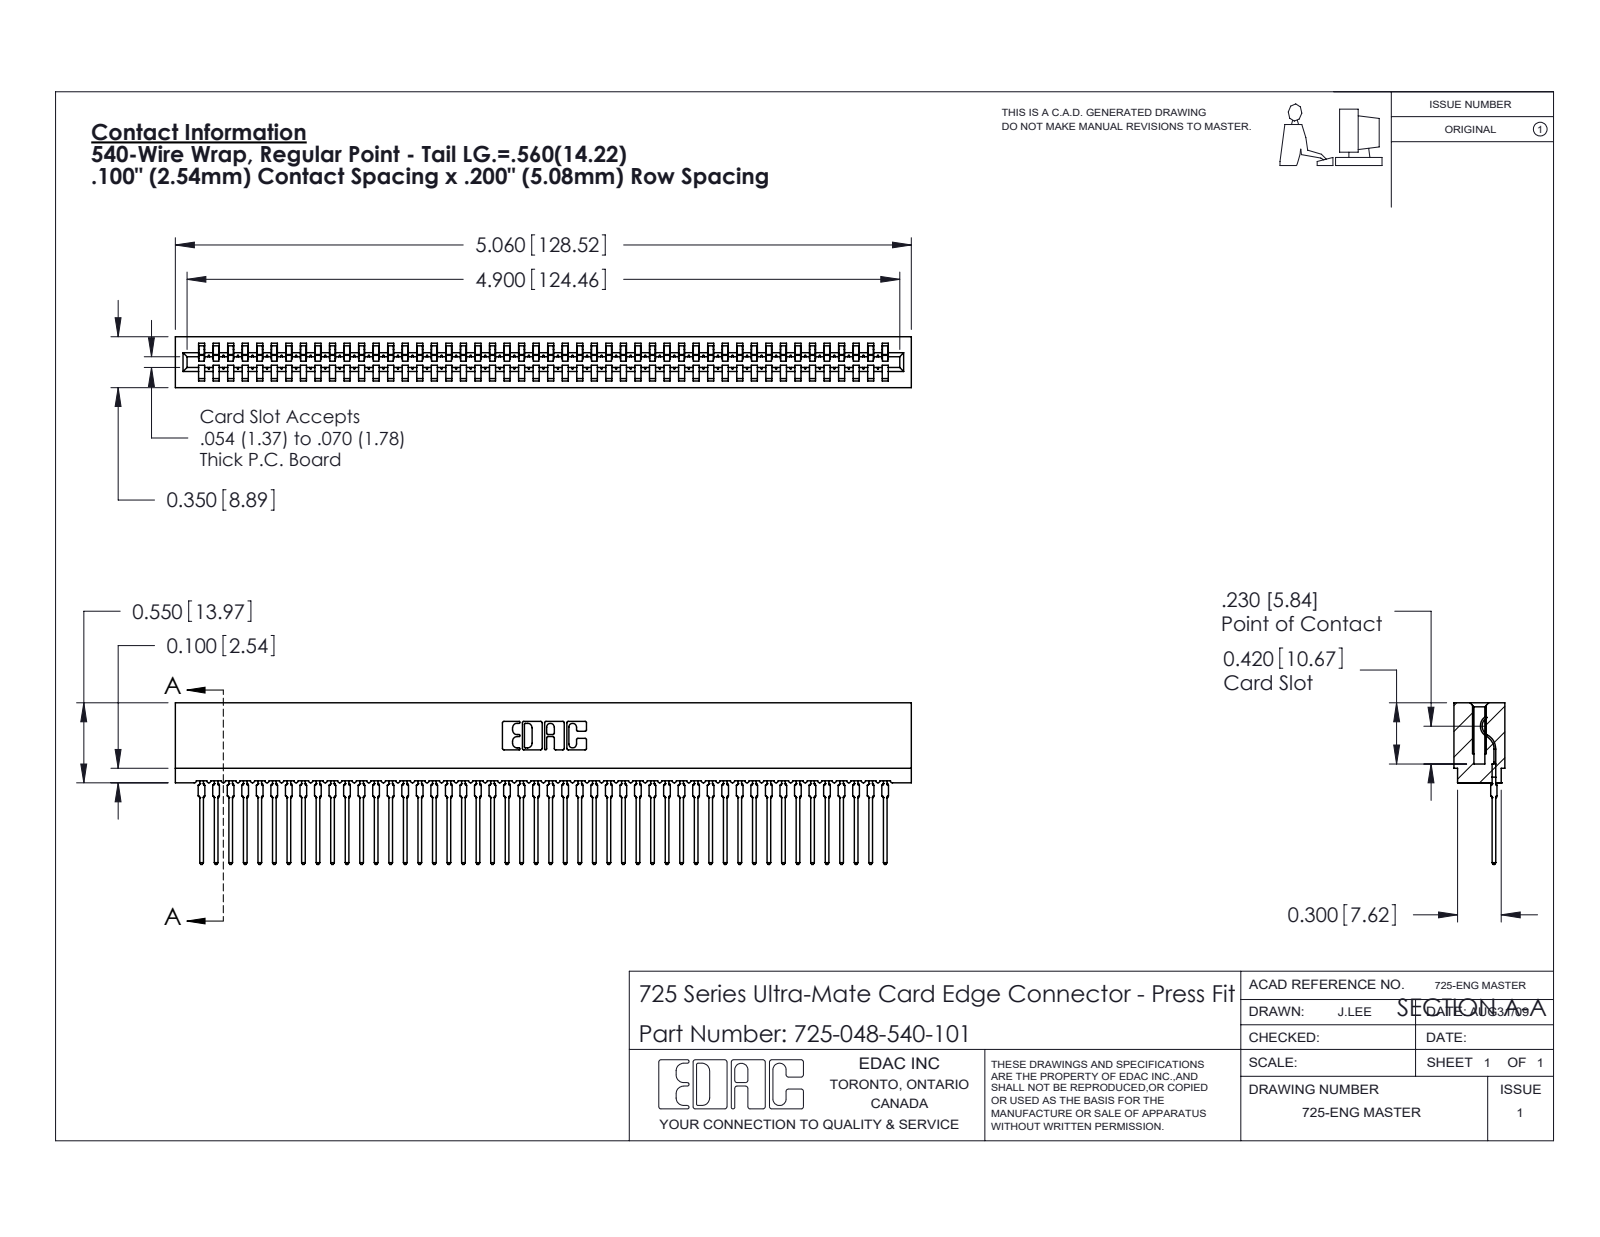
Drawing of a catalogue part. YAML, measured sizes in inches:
part_name: "725 Part_Insulator Option - 01; 725-048-540-101; 745-292-001_540"
step_written_by: "SolidWorks 2020 (CONFIG_CONTROL_DESIGN)"
units: inches
bodies: {solids: 49, faces: 5471, planar: 3271, cylindrical: 952, other: 1248}
overall_size: [5.06, 1.111, 0.35]
volume: 0.6
surface_area: 30.32
partial_cylinders:
  - {radius: 0.015, count: 96}
  - {radius: 0.021, count: 96}
  - {radius: 0.01, count: 22}
  - {radius: 0.007, count: 6}
  - {radius: 0.031, count: 6}
  - {radius: 0.005, count: 4}
  - {radius: 0.011, count: 4}
  - {radius: 0.026, count: 3}
face_to_face_distances: [0.35, 0.2, 0.212, 0.138, 0.063, 0.287, 0.045, 0.305, 0.093, 0.167]
